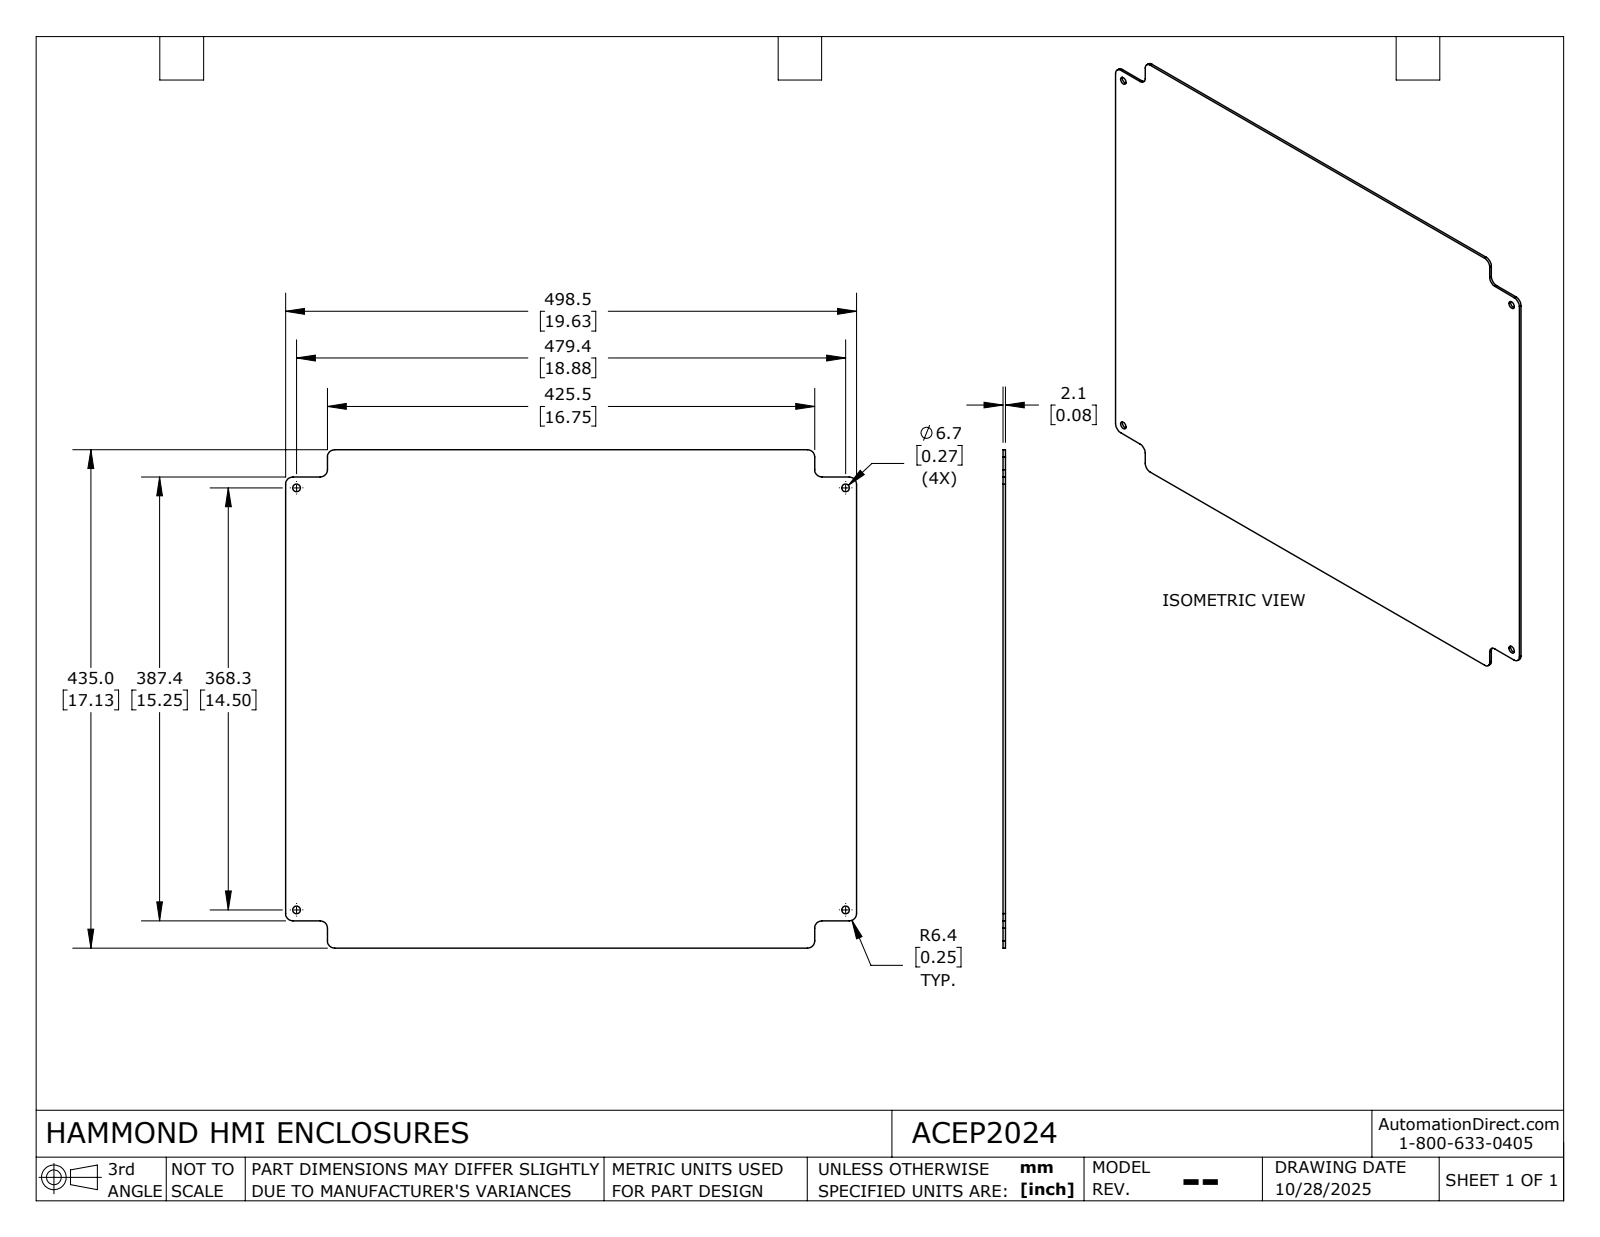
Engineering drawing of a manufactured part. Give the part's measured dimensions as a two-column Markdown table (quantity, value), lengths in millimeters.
| quantity | value |
| --- | --- |
| part name | ACEP2024 |
| STEP written by | SolidWorks 2024 (AUTOMOTIVE_DESIGN) |
| units | millimeters |
| bodies | 1 solid, 30 faces (14 planar, 16 cylindrical, 0 other) |
| overall size | 498.48 × 434.98 × 2.06 |
| volume | 438 575 mm³ |
| surface area | 430 286 mm² |
| round holes (diameter × count) | 6.73 × 4 |
| partial cylindrical surfaces (radius × count) | 6.35 × 12 |
| main face-to-face distances | 2.06, 434.98, 498.48, 23.81, 411.17, 387.36, 36.52, 461.96, 425.44 |
| hole center spacings | 368.3, 479.42, 604.56 |
